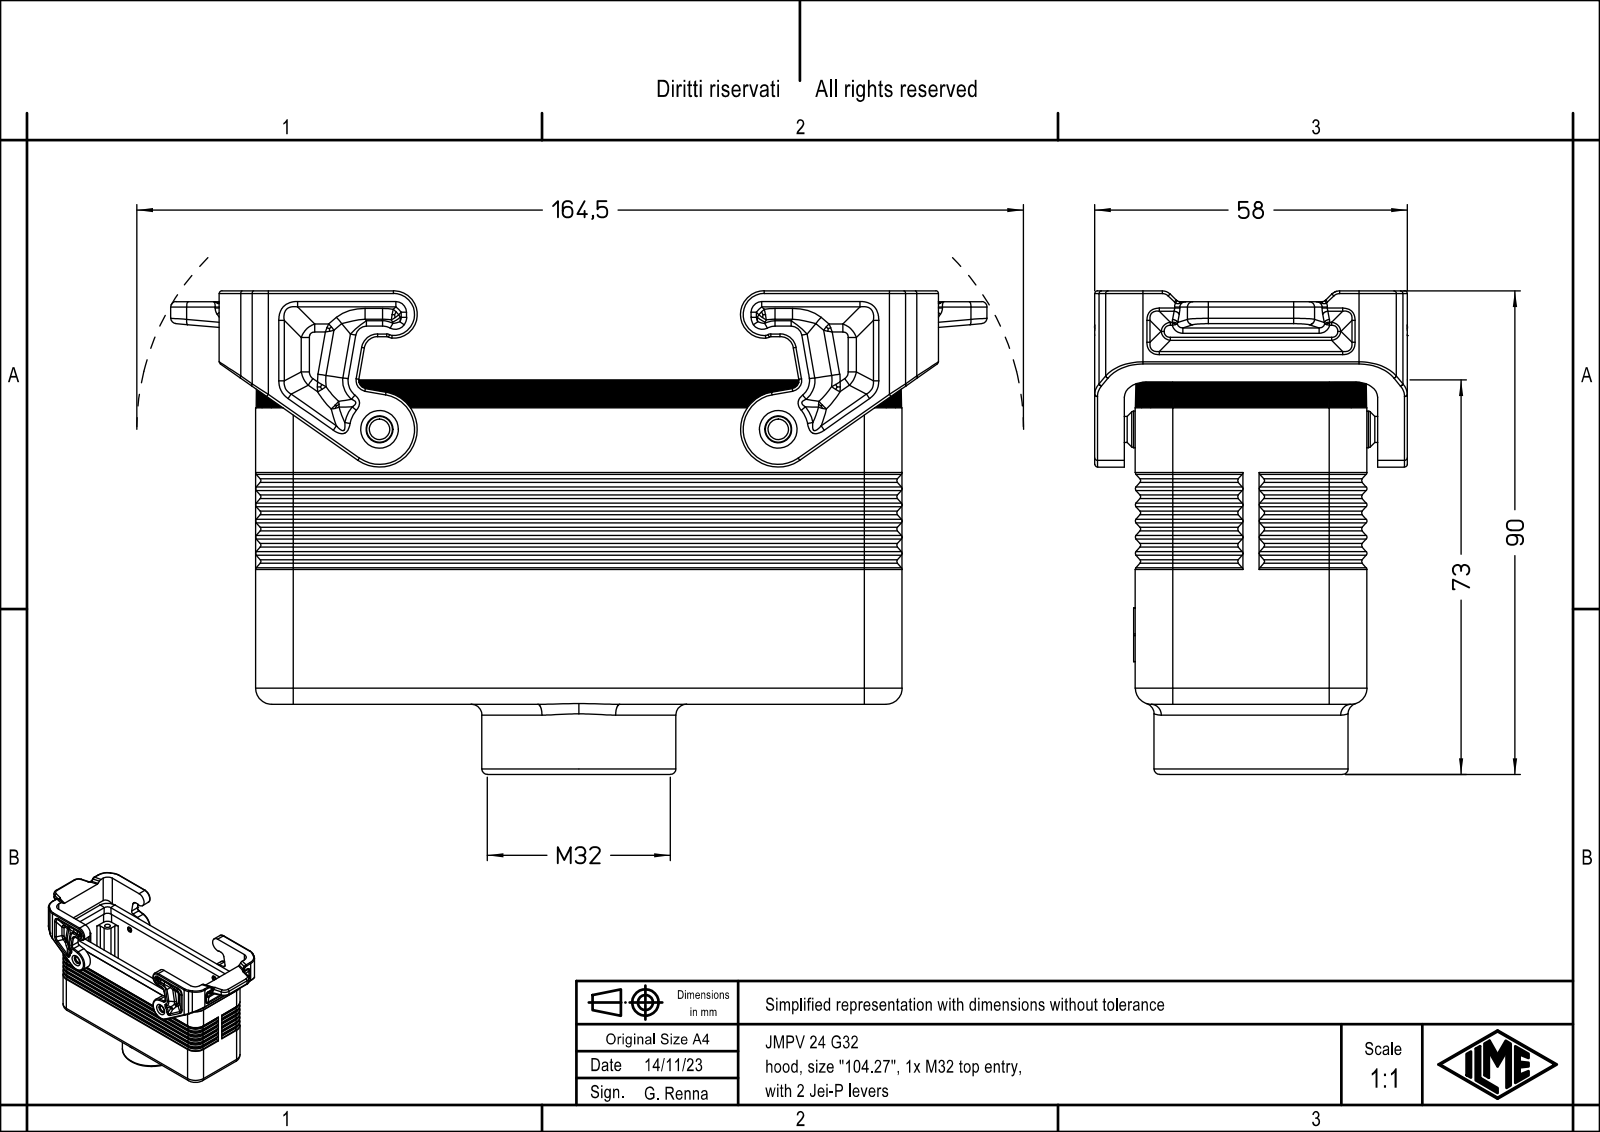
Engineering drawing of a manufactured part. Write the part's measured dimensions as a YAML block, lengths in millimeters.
part_name: "JMPV 24 G32"
step_written_by: "Creo Elements/Direct Modeling 20.1B 02-Apr-2019 (C) Parametric Technology GmbH (AUTOMOTIVE_DESIGN)"
units: millimeters
bodies: {solids: 1, faces: 1151, planar: 282, cylindrical: 391, other: 478}
overall_size: [151.5, 89.7, 58.08]
volume: 108471
surface_area: 62112
round_holes:
  - {diameter: 3, count: 4}
  - {diameter: 3.5, count: 4}
  - {diameter: 4.8, count: 2}
  - {diameter: 28, count: 1}
  - {diameter: 30.6, count: 1}
round_bosses_or_shafts:
  - {diameter: 6.8, count: 2}
  - {diameter: 36, count: 1}
partial_cylinders:
  - {radius: 0.5, count: 102}
  - {radius: 3, count: 34}
  - {radius: 1, count: 32}
  - {radius: 1.5, count: 26}
  - {radius: 2, count: 20}
  - {radius: 0.33, count: 15}
  - {radius: 4, count: 12}
  - {radius: 6, count: 12}
face_to_face_distances: [3.5, 39.5, 2, 36, 43, 5.5, 2.8, 41.5, 45, 47]
hole_center_spacings: [53.72, 27, 104, 107.45, 74]
